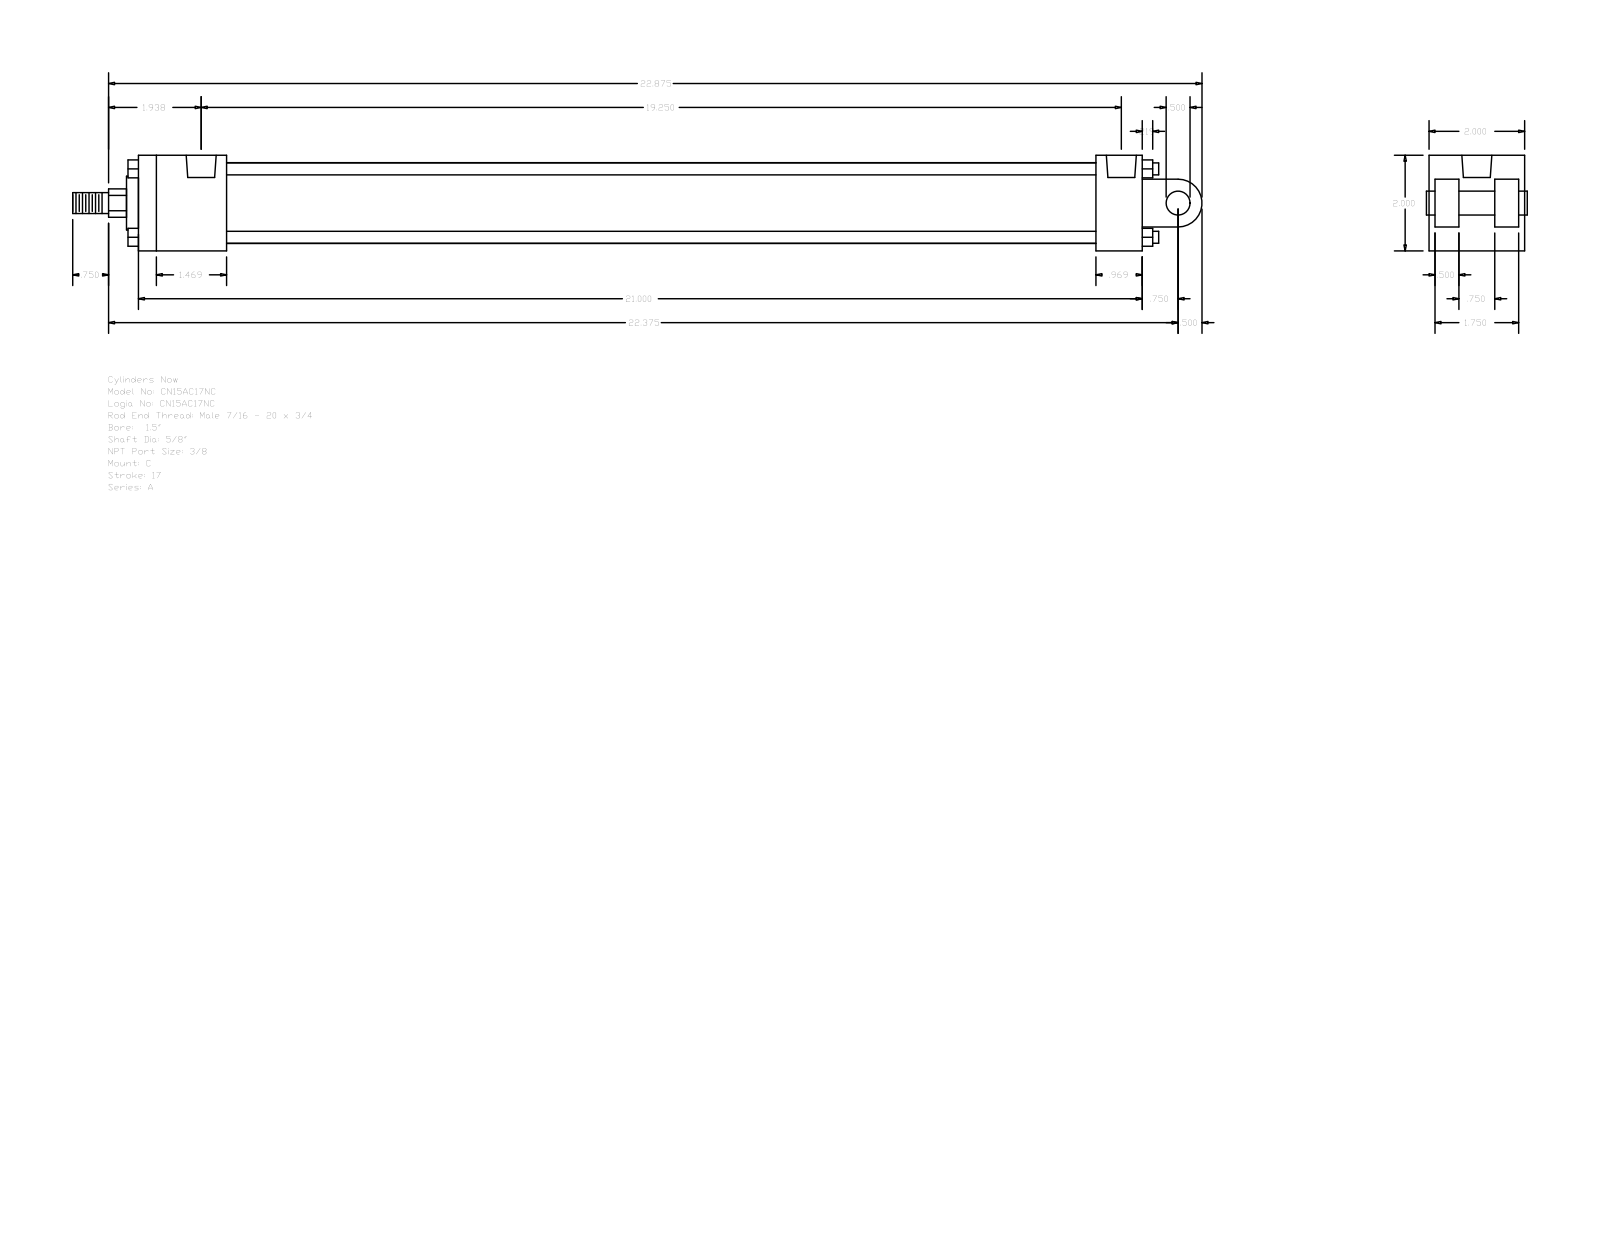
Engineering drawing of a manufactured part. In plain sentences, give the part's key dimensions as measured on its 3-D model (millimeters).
The part is named "A_C__0150_0.625". Its 3-D file was written by "GSSL Pune (CONFIG_CONTROL_DESIGN)". It is 0 solids with 135 faces: 102 planar, 33 cylindrical and 0 other. Overall it measures 600.08 by 50.8 by 50.8 millimeters. Round holes: 4 of diameter 5.56, 2 of diameter 15.93. Round bosses or shafts: 4 of diameter 6.35, 1 of diameter 42.93, 1 of diameter 28.57, 1 of diameter 15.88, 1 of diameter 12.7, 1 of diameter 11.11. Partial cylindrical surfaces (rounded edges, fillets, slot ends): 1 of radius 7.54, 1 of radius 12.7. The main face-to-face distances are 50.8, 12.7, 533.39, 34.93, 3.17, 47.63, 15.87, 31.76, 508.79, 24.6. The hole center spacings are 3.97, 481.01, 484.98, 488.95.
